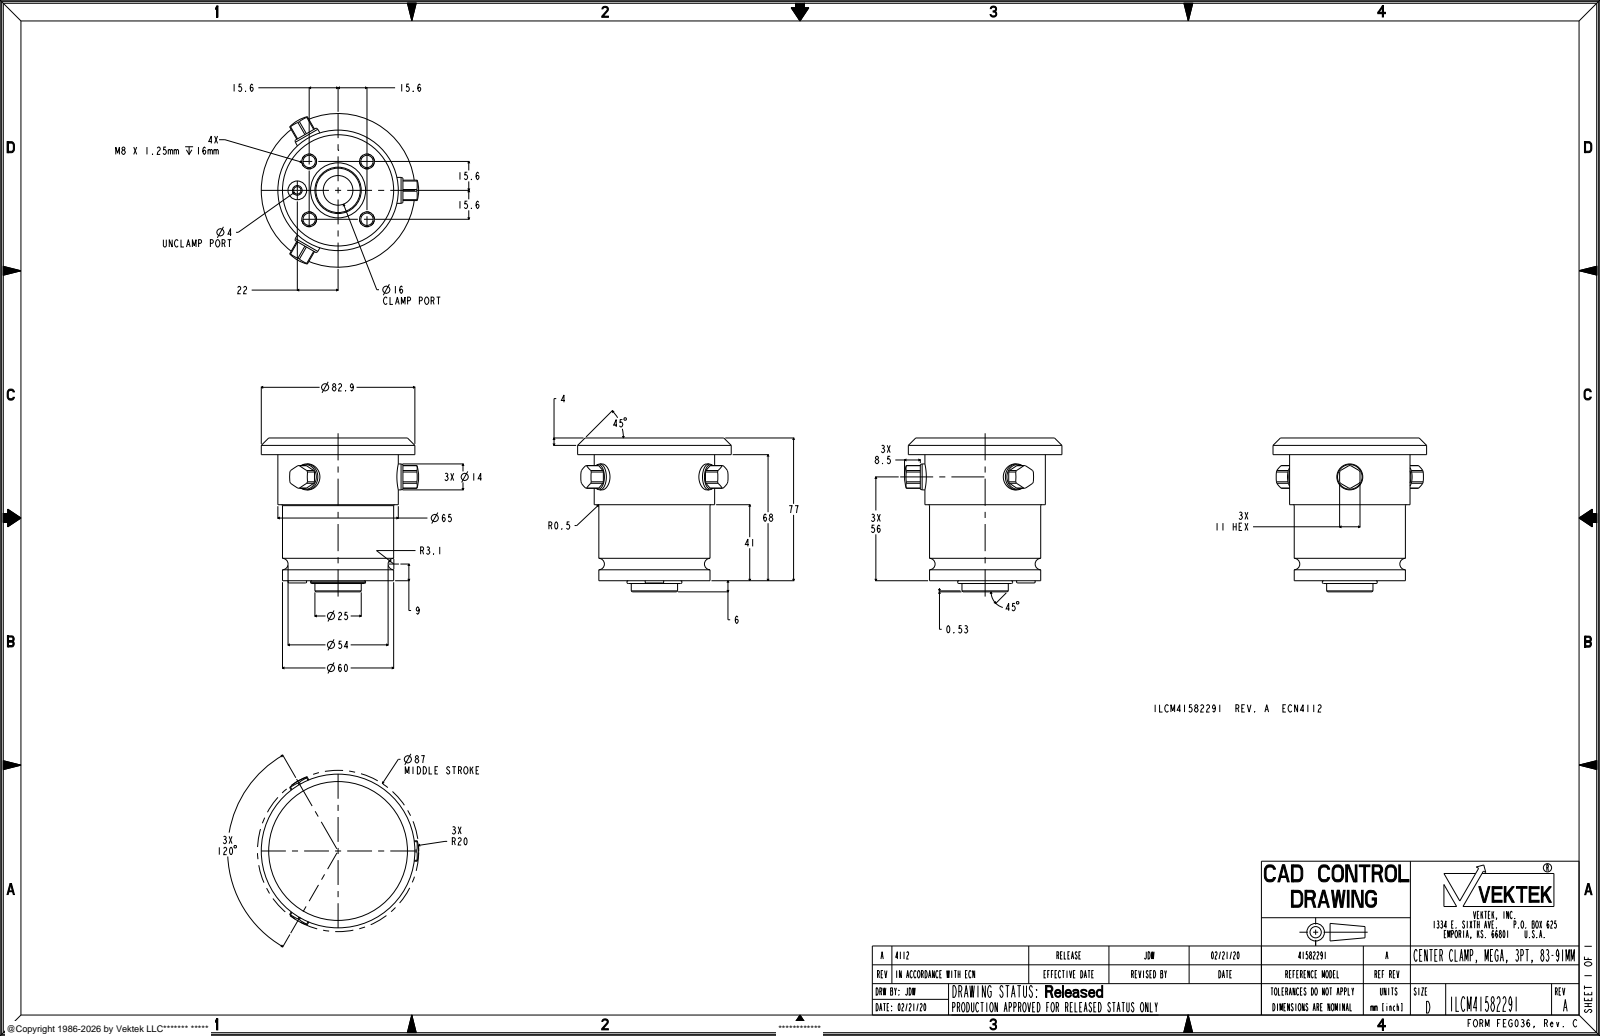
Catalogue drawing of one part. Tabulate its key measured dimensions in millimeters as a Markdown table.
| quantity | value |
| --- | --- |
| part name | ILCM41582291 |
| STEP written by | PRO/ENGINEER BY PARAMETRIC TECHNOLOGY CORPORATION, 2013320 (AUTOMOTIVE_DESIGN) |
| units | millimeters |
| bodies | 1 solid, 158 faces (46 planar, 64 cylindrical, 48 other) |
| overall size | 84.95 × 83 × 82.9 |
| volume | 252 122 mm³ |
| surface area | 32 888 mm² |
| round holes (diameter × count) | 6.65 × 4, 14 × 3, 4 × 1, 16 × 1 |
| round bosses / shafts (diameter × count) | 8 × 4, 82.9 × 1, 65 × 1, 60 × 1, 29.7 × 1, 25 × 1 |
| partial cylindrical surfaces (radius × count) | 6.1 × 3 |
| main face-to-face distances | 77, 68, 9, 2.5, 3, 41, 27, 36, 11, 6 |
| hole center spacings | 22.06, 31.2, 16.86, 40.71, 44.12, 22 |
